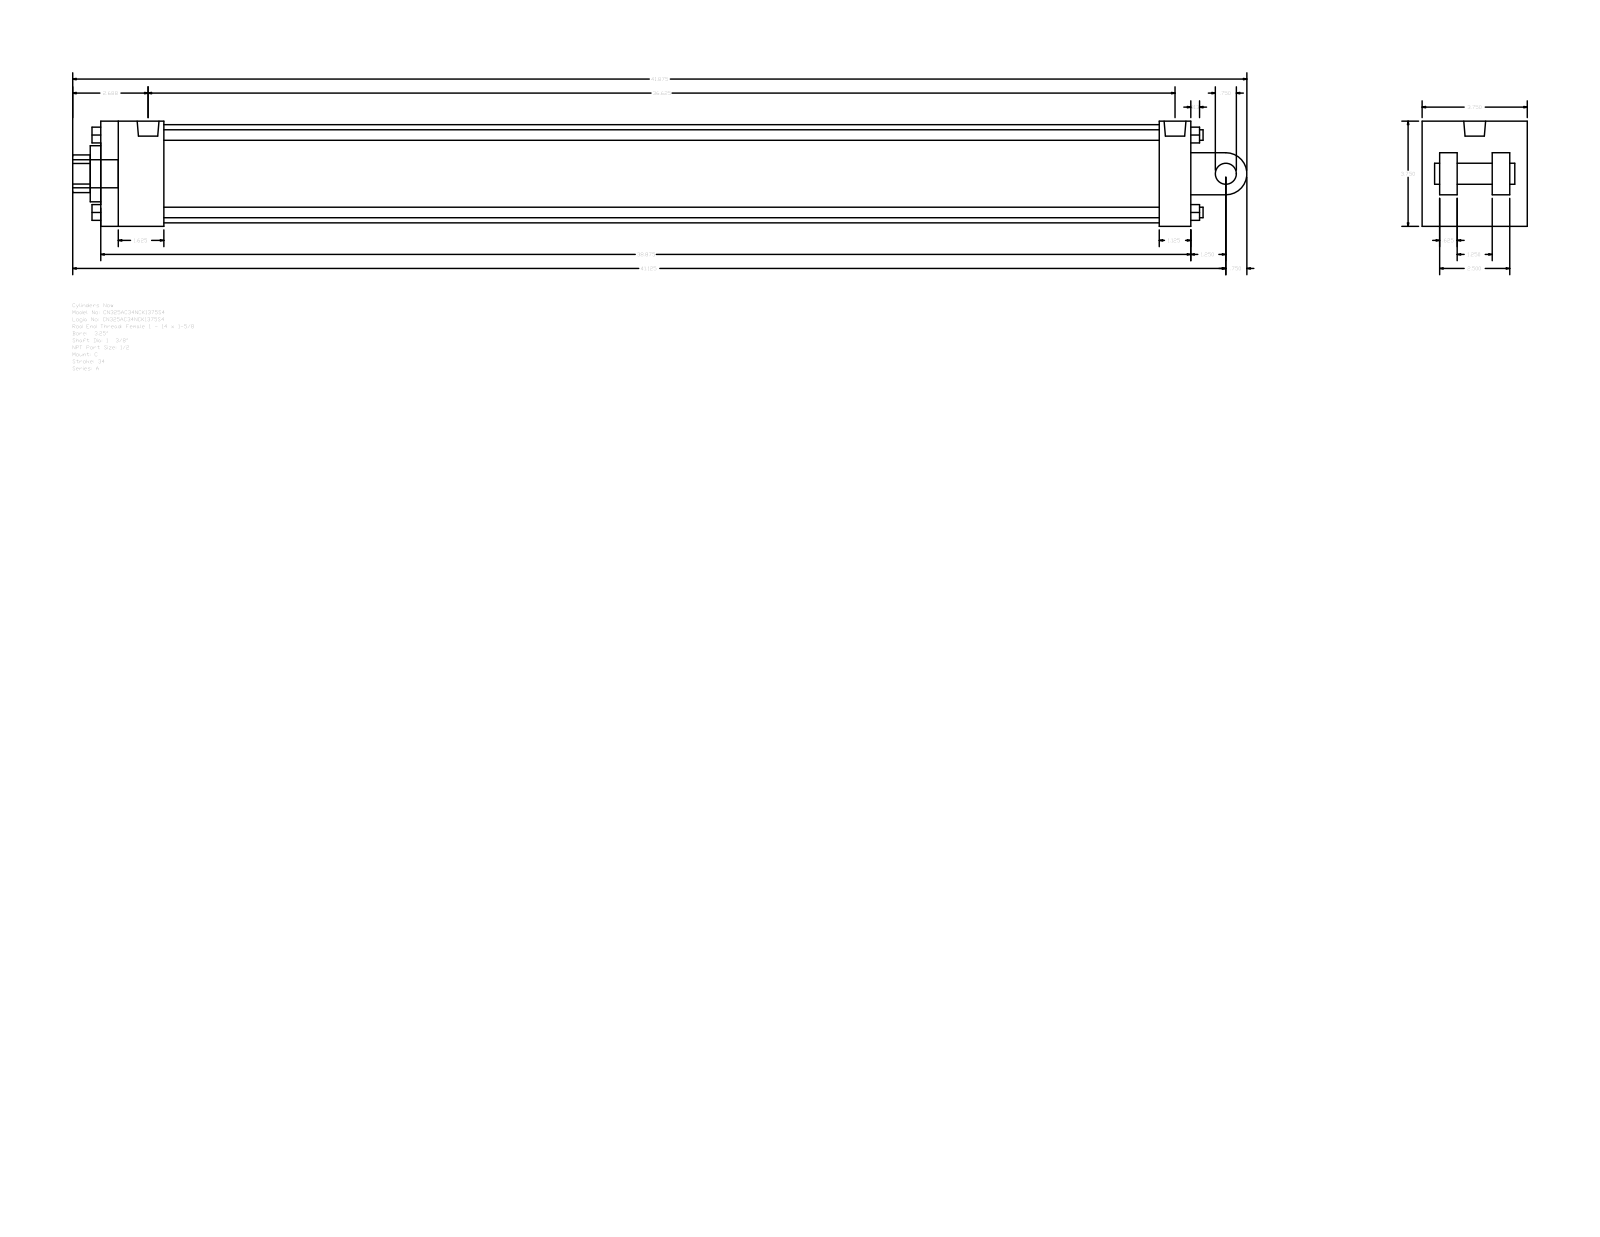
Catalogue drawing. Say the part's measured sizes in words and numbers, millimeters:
The part is named "A_C__0325_1.375". Its 3-D file was written by "GSSL Pune (CONFIG_CONTROL_DESIGN)". It is 0 solids with 135 faces: 102 planar, 33 cylindrical and 0 other. Overall it measures 1063.62 by 95.25 by 95.25 millimeters. Round holes: 2 of diameter 8.73, 1 of diameter 19.77, 1 of diameter 34.92, 1 of diameter 50.8, 1 of diameter 88.9. Round bosses or shafts: 4 of diameter 9.53, 2 of diameter 8.73, 1 of diameter 25.4, 1 of diameter 19.77, 1 of diameter 19.05. Partial cylindrical surfaces (rounded edges, fillets, slot ends): 1 of radius 17.06, 1 of radius 19.05. The main face-to-face distances are 95.24, 15.87, 987.43, 63.5, 66.67, 28.58, 31.74, 79.37, 47.63, 958.85. The hole center spacings are 3.18.
